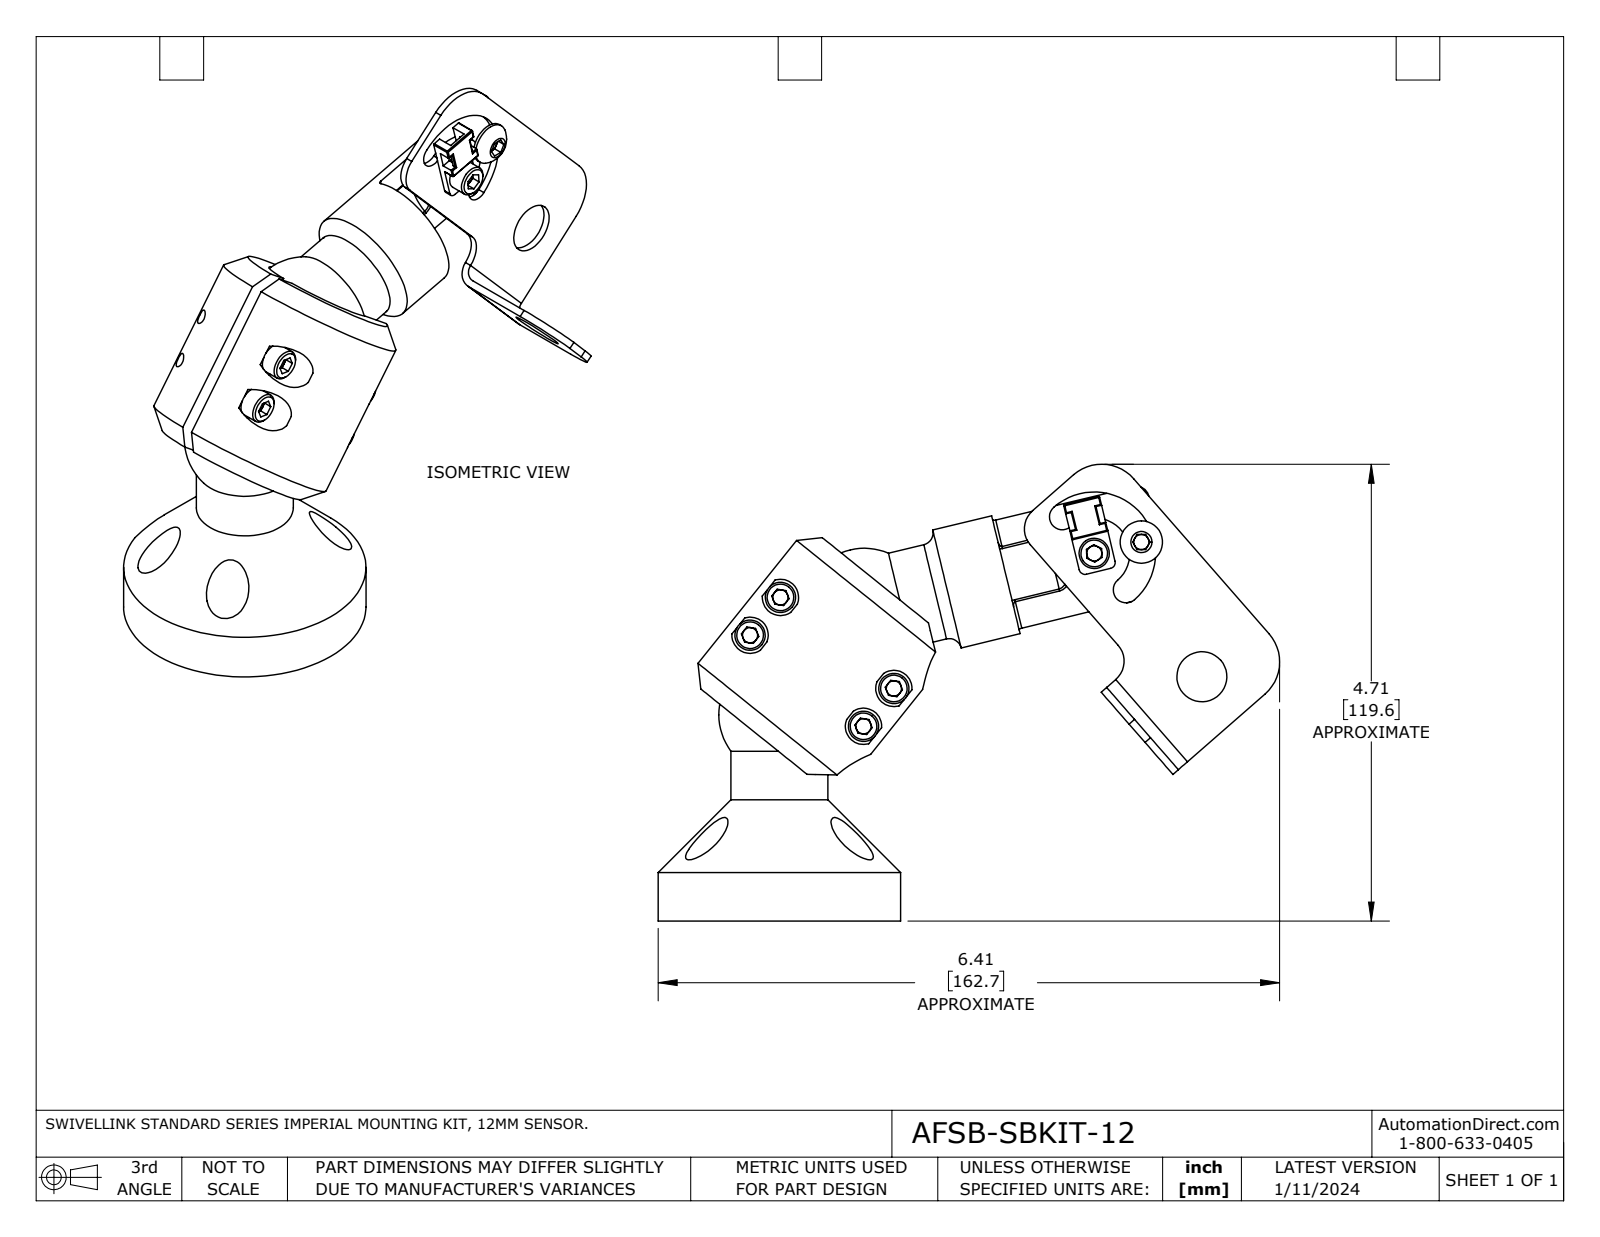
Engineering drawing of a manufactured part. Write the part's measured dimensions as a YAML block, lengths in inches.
part_name: "AFSB-SBKIT-12"
step_written_by: "SolidWorks 2023 (AUTOMOTIVE_DESIGN)"
units: inches
bodies: {solids: 12, faces: 294, planar: 155, cylindrical: 89, other: 50}
overall_size: [6.408, 4.737, 2.425]
volume: 6.565
surface_area: 85.22
round_holes:
  - {diameter: 0.15, count: 5}
  - {diameter: 0.221, count: 4}
  - {diameter: 0.281, count: 4}
  - {diameter: 0.437, count: 4}
  - {diameter: 0.375, count: 2}
  - {diameter: 0.375, count: 2}
  - {diameter: 0.516, count: 2}
  - {diameter: 0.2, count: 1}
  - {diameter: 0.201, count: 1}
  - {diameter: 0.281, count: 1}
  - {diameter: 0.75, count: 1}
  - {diameter: 0.875, count: 1}
round_bosses_or_shafts:
  - {diameter: 0.313, count: 5}
  - {diameter: 0.19, count: 5}
  - {diameter: 1, count: 2}
  - {diameter: 2.5, count: 1}
  - {diameter: 1.98, count: 1}
  - {diameter: 1.25, count: 1}
  - {diameter: 0.437, count: 1}
  - {diameter: 0.25, count: 1}
partial_cylinders:
  - {radius: 0.01, count: 12}
  - {radius: 0.438, count: 3}
  - {radius: 0.063, count: 2}
  - {radius: 0.133, count: 2}
  - {radius: 0.25, count: 2}
  - {radius: 0.525, count: 2}
  - {radius: 0.562, count: 2}
  - {radius: 0.03, count: 1}
face_to_face_distances: [0.074, 0.125, 0.113, 0.187, 0.075, 0.238, 0.312, 2, 0.341, 0.465]
hole_center_spacings: [0.902, 0.5, 1.5, 1, 1.581, 1.803, 1.5, 1.522]
